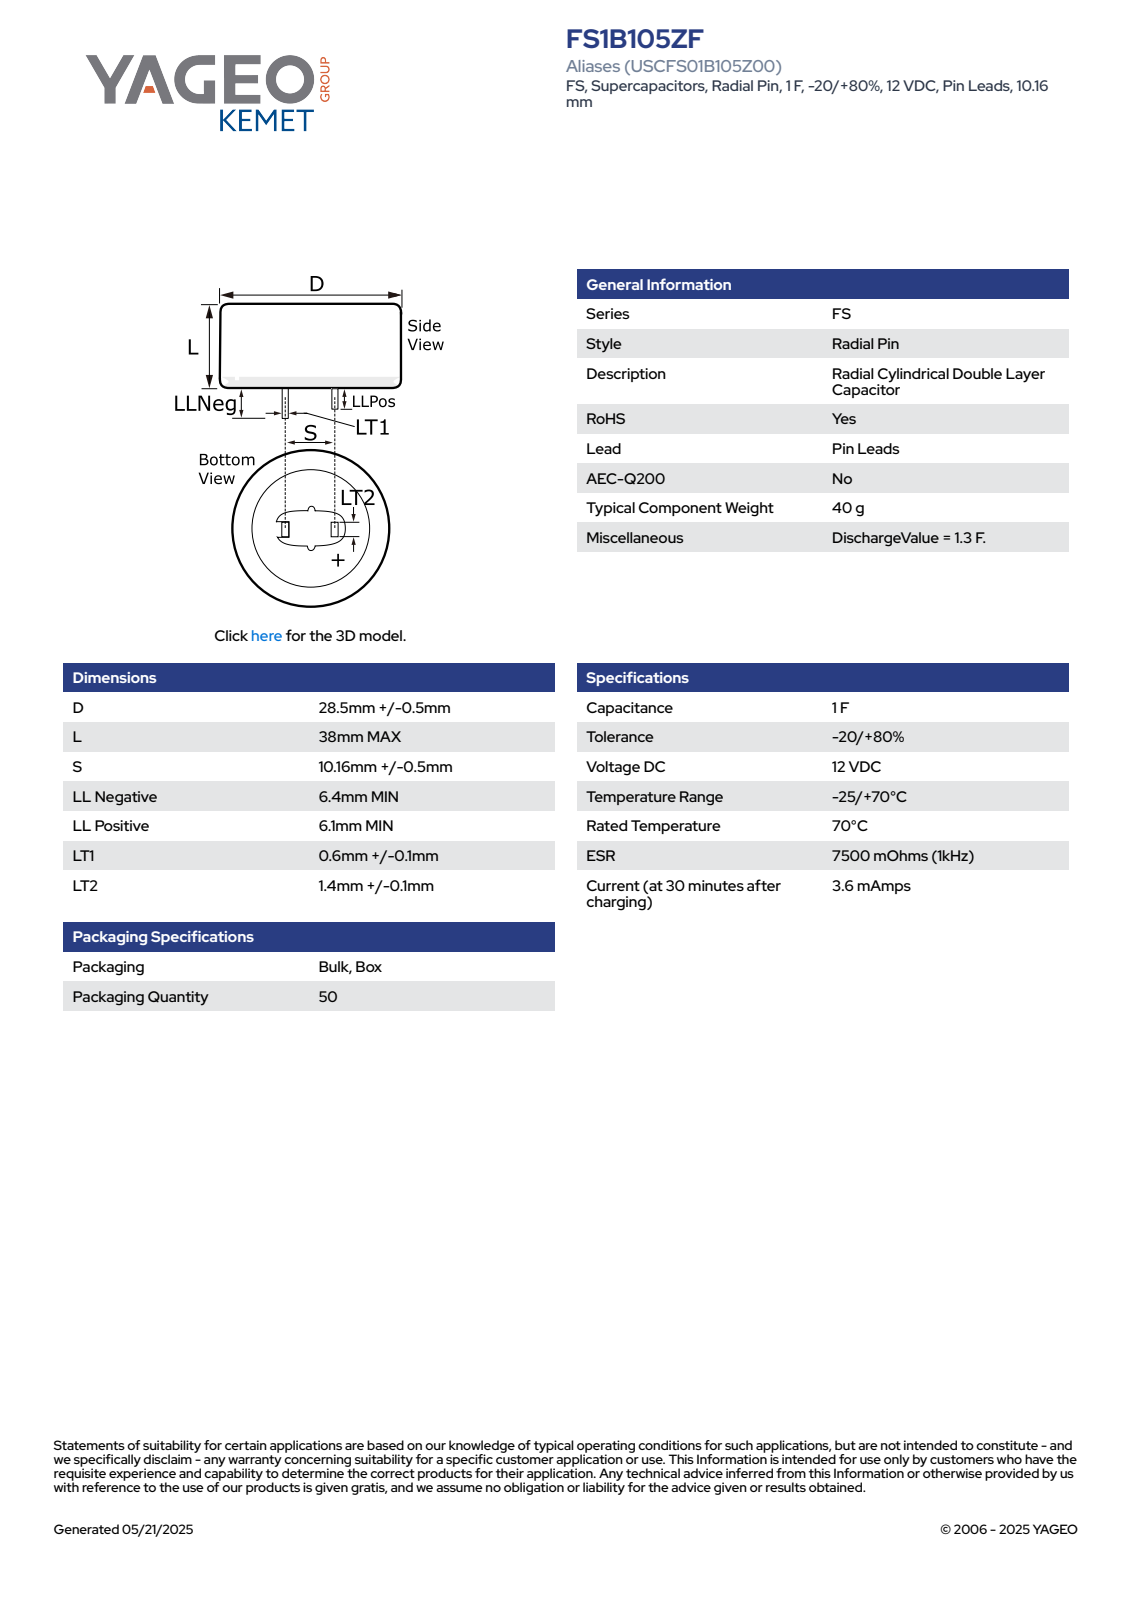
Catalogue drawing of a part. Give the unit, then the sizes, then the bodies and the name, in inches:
Units: inches
Overall size (bounding box): 1.748 × 1.142 × 1.142
Round bosses / shafts (diameter × count): ⌀1.142 ×1
Partial cylindrical surfaces — rounded edges, fillets, slot ends (radius × count): R0.571 ×1
Main face-to-face distances: 1.496, 0.028, 0.4, 0.372, 0.428, 0.059, 0.252, 1.748, 0.24, 1.736
Volume: 1.519 in³ · Surface area: 7.195 in²
Bodies: 1 solid, 78 faces (70 planar, 4 cylindrical, 4 other)
Part name (STEP PRODUCT): CDR_LPLLN_D29L38S10.16LLNEG6.4LLPOS6.1LT10.7LT21.5
STEP written by: SolidWorks 2014 (AUTOMOTIVE_DESIGN)
